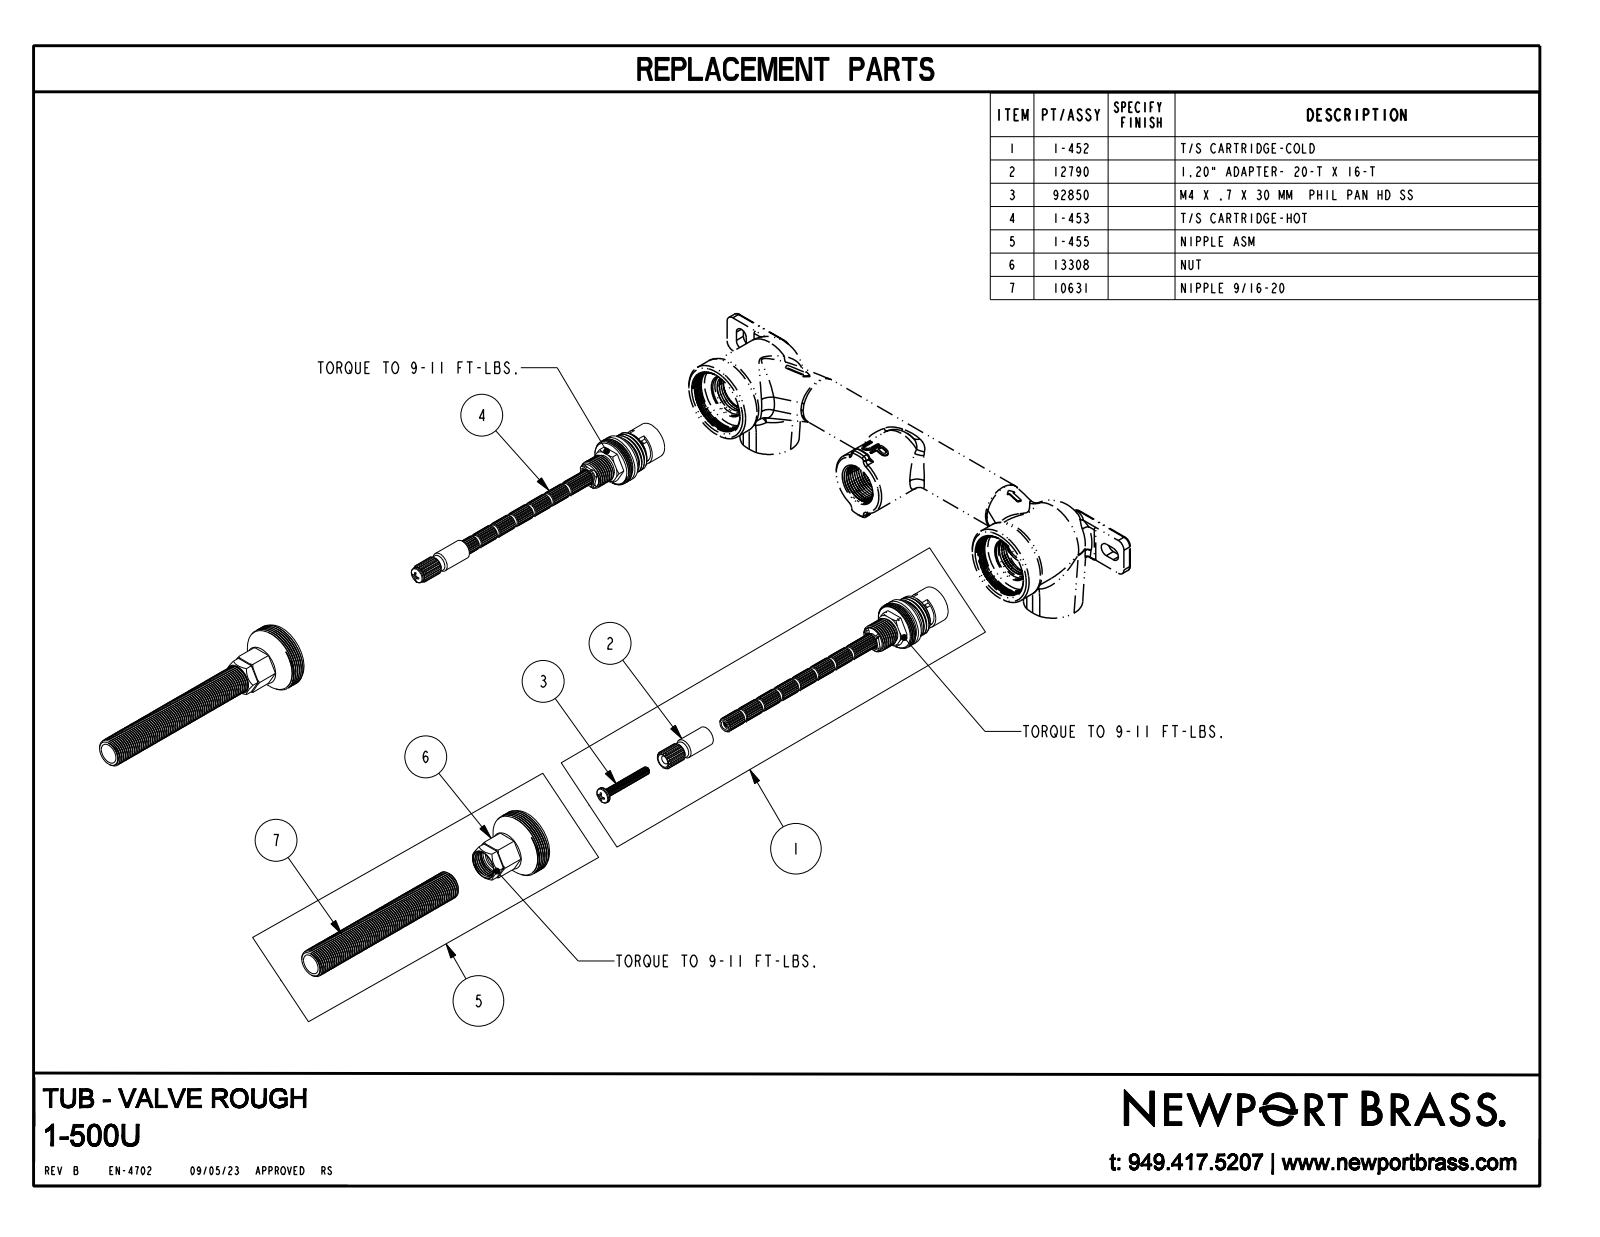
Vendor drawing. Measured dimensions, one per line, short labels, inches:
name: 1-500U
written by: CREO PARAMETRIC BY PTC INC, 2018400 (AUTOMOTIVE_DESIGN)
unit: in
bodies: 4 solids, 6265 faces (5474 planar, 501 cylindrical, 290 other)
size: 11.024 × 9.4 × 2.82
volume: 26.83 in³; area: 114.7 in²
holes: 2× ⌀0.172, 2× ⌀0.33, 1× ⌀1
bosses: 2× ⌀1.575, 2× ⌀1.417, 2× ⌀0.84, 2× ⌀0.563, 2× ⌀0.391, 2× ⌀0.325, 2× ⌀0.315, 2× ⌀0.157
rounds: 8× R0.039, 8× R0.079, 6× R0.079, 6× R0.157, 2× R0.039, 2× R0.046, 2× R0.05, 2× R0.137
face distances: 2.087, 9.503, 0.197, 1.89, 1.574, 1.575, 1.579, 1.57, 6.087, 5.89
hole spacings: 7.874
